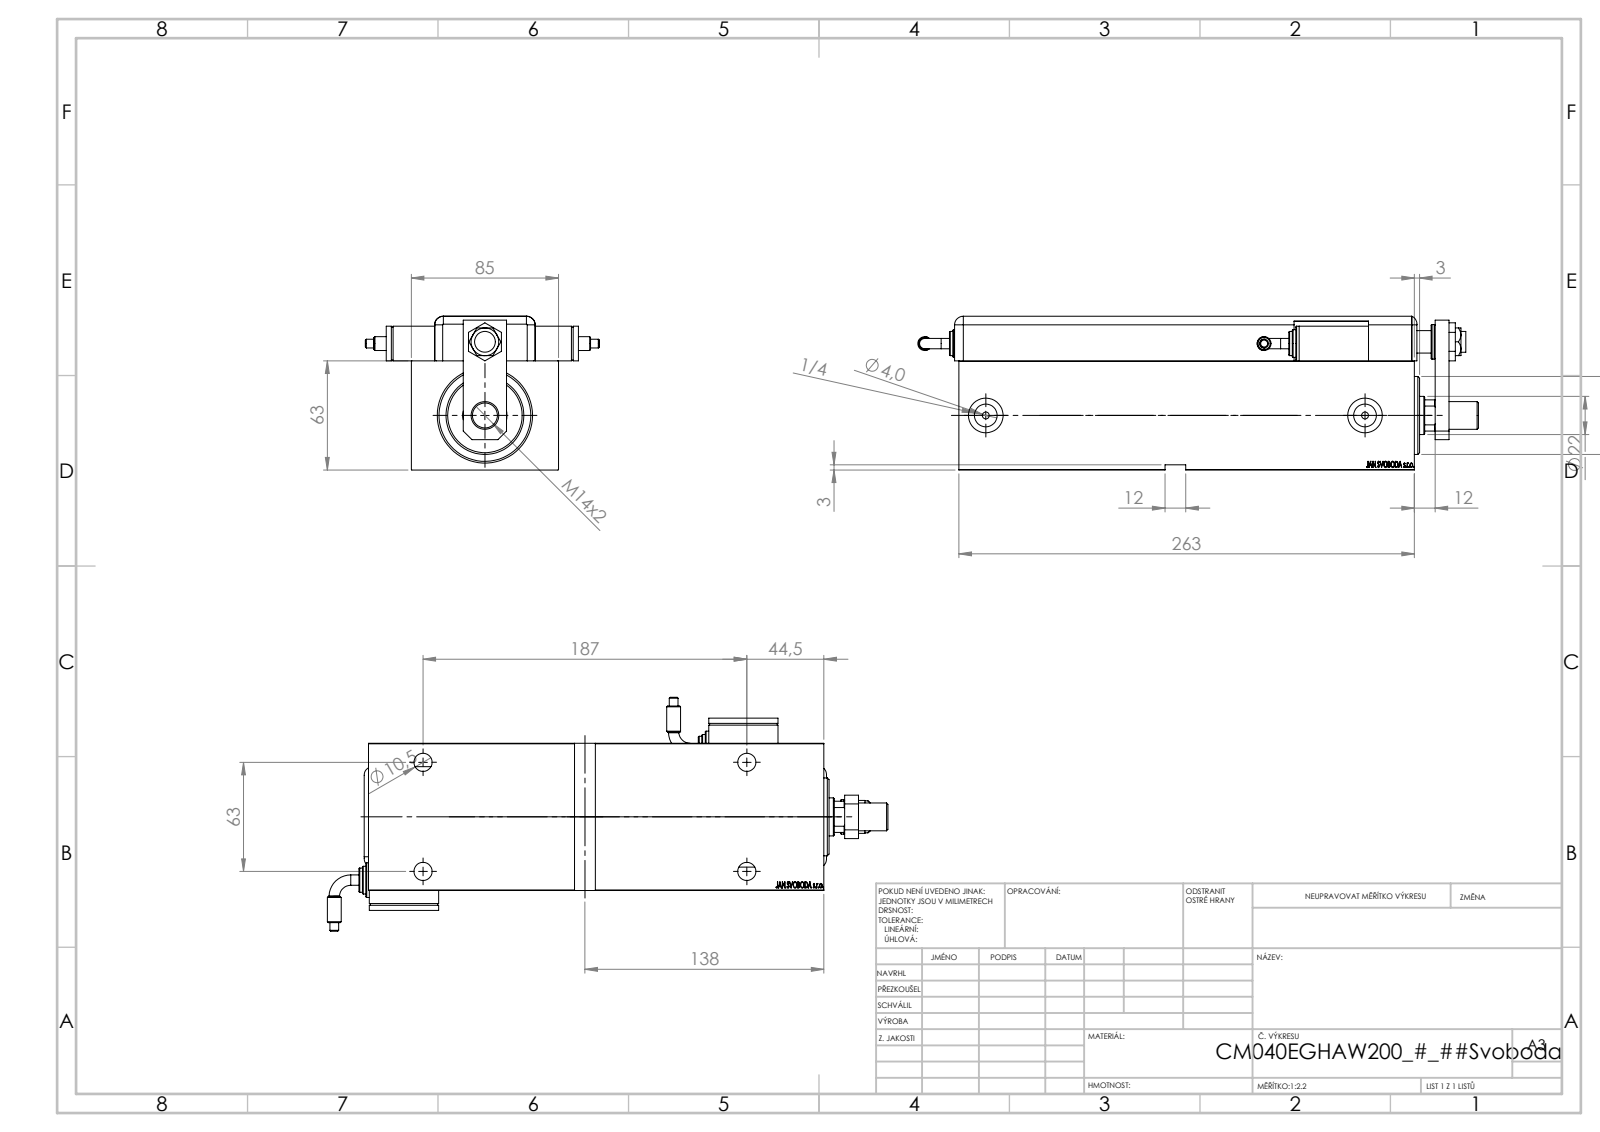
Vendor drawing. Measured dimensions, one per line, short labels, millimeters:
name: SWITCH DIM A_G; MAGNETIC SWITCH Q; V450CM_MALE_METRIC; V450CM_VC_B (+7 more)
written by: SolidWorks 2019 (CONFIG_CONTROL_DESIGN)
unit: mm
bodies: 9 solids, 1257 faces (616 planar, 109 cylindrical, 532 other)
size: 323.76 × 135.01 × 88.8
volume: 1 321 000 mm³; area: 256 716 mm²
holes: 4× ⌀4, 4× ⌀10.5, 4× ⌀16.5, 2× ⌀8, 2× ⌀13.16, 2× ⌀14, 2× ⌀20, 1× ⌀12, 1× ⌀12.5, 1× ⌀13, 1× ⌀40, 1× ⌀53
bosses: 3× ⌀20, 2× ⌀8, 2× ⌀5.04, 1× ⌀45, 1× ⌀42, 1× ⌀22, 1× ⌀16
rounds: 9× R5, 3× R7, 2× R3, 2× R8, 1× R10, 1× R10.5, 1× R12.75
face distances: 3, 63, 85, 88.8, 25.8, 13.5, 85.8, 22.8, 16.5, 71.5
hole spacings: 41.5, 54.61, 63, 187, 197.33, 223.54, 226.34, 1
